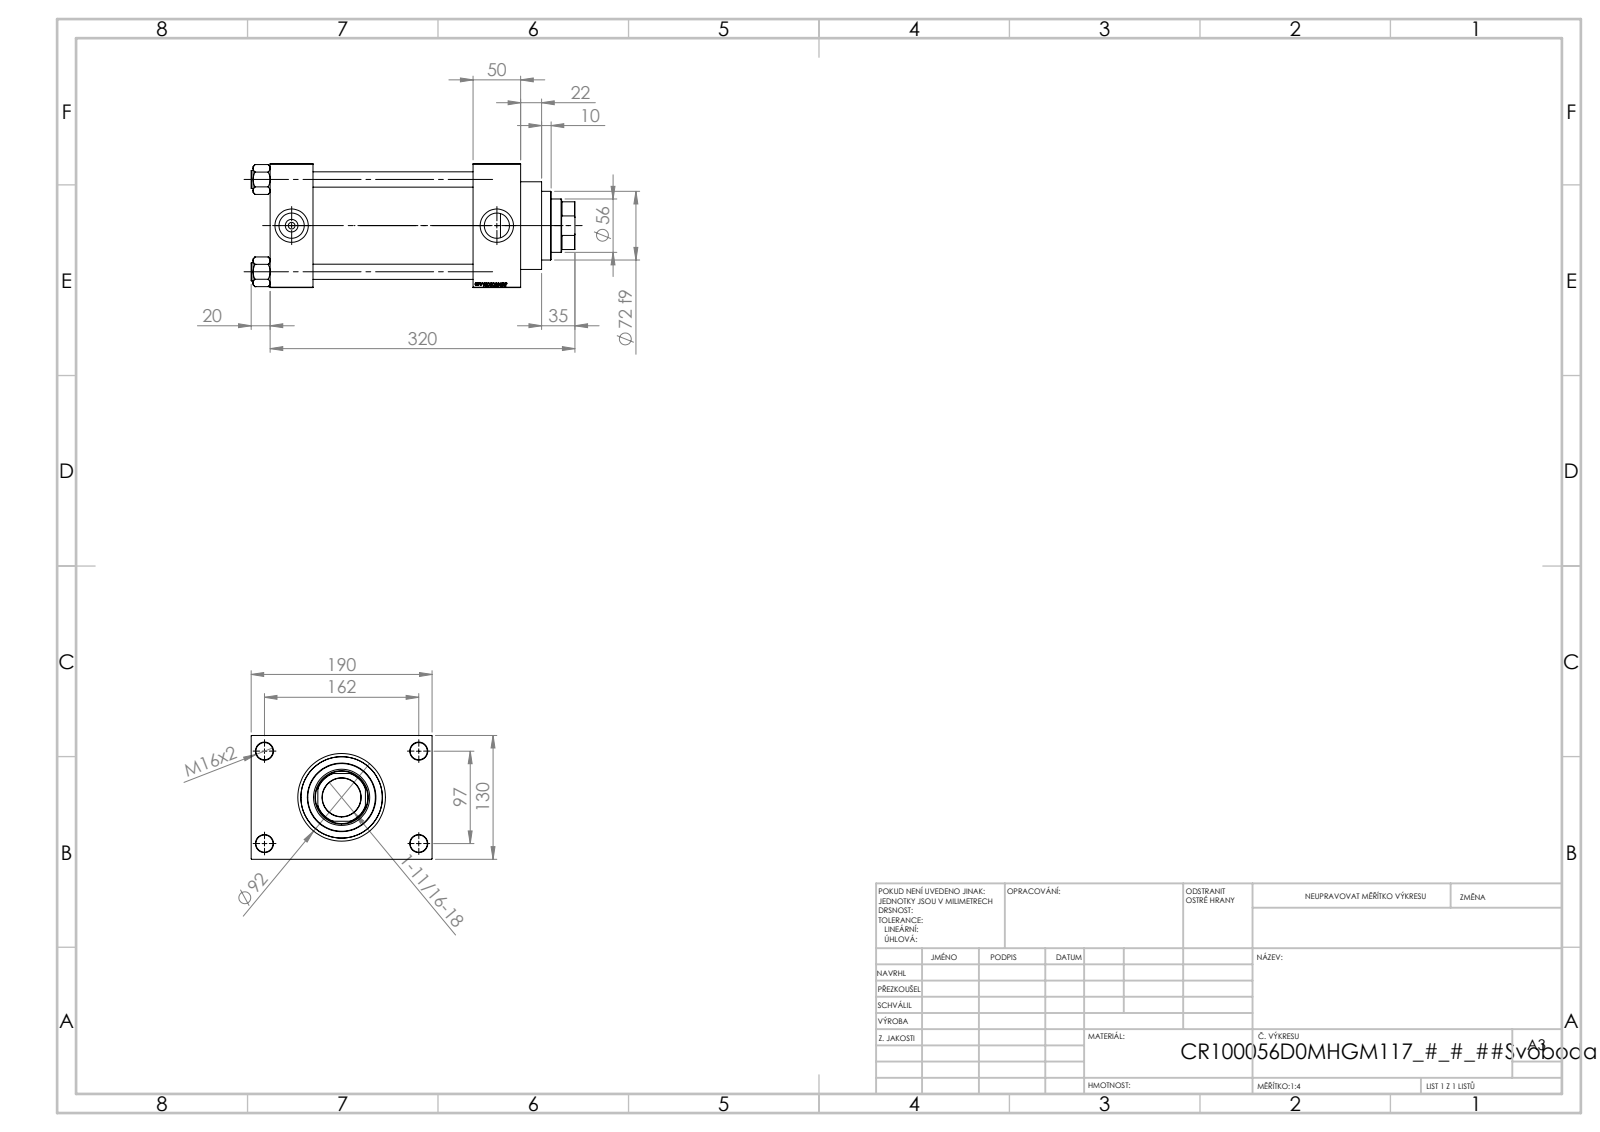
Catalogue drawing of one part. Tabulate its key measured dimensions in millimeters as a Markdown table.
| quantity | value |
| --- | --- |
| part name | NUT_M5_D; V215_VC_A; V215CR_D_TYCINKA; V215CR_VCP_D (+1 more) |
| STEP written by | SolidWorks 2019 (CONFIG_CONTROL_DESIGN) |
| units | millimeters |
| bodies | 11 solids, 1151 faces (545 planar, 88 cylindrical, 518 other) |
| overall size | 340 × 190 × 130 |
| volume | 3 039 000 mm³ |
| surface area | 461 707 mm² |
| round holes (diameter × count) | 16 × 4, 18 × 4, 7 × 2, 26.44 × 2, 35 × 2, 40.5 × 1, 56 × 1, 59 × 1, 76 × 1, 85.5 × 1, 100 × 1 |
| round bosses / shafts (diameter × count) | 19 × 4, 106 × 1, 92 × 1, 72 × 1 |
| partial cylindrical surfaces (radius × count) | 27 × 1 |
| main face-to-face distances | 130, 50, 45, 213, 168, 263, 218, 30, 160, 190 |
| hole center spacings | 32.55, 68.52, 94.41, 96.9, 102.27, 129.45, 161.73, 97 |
